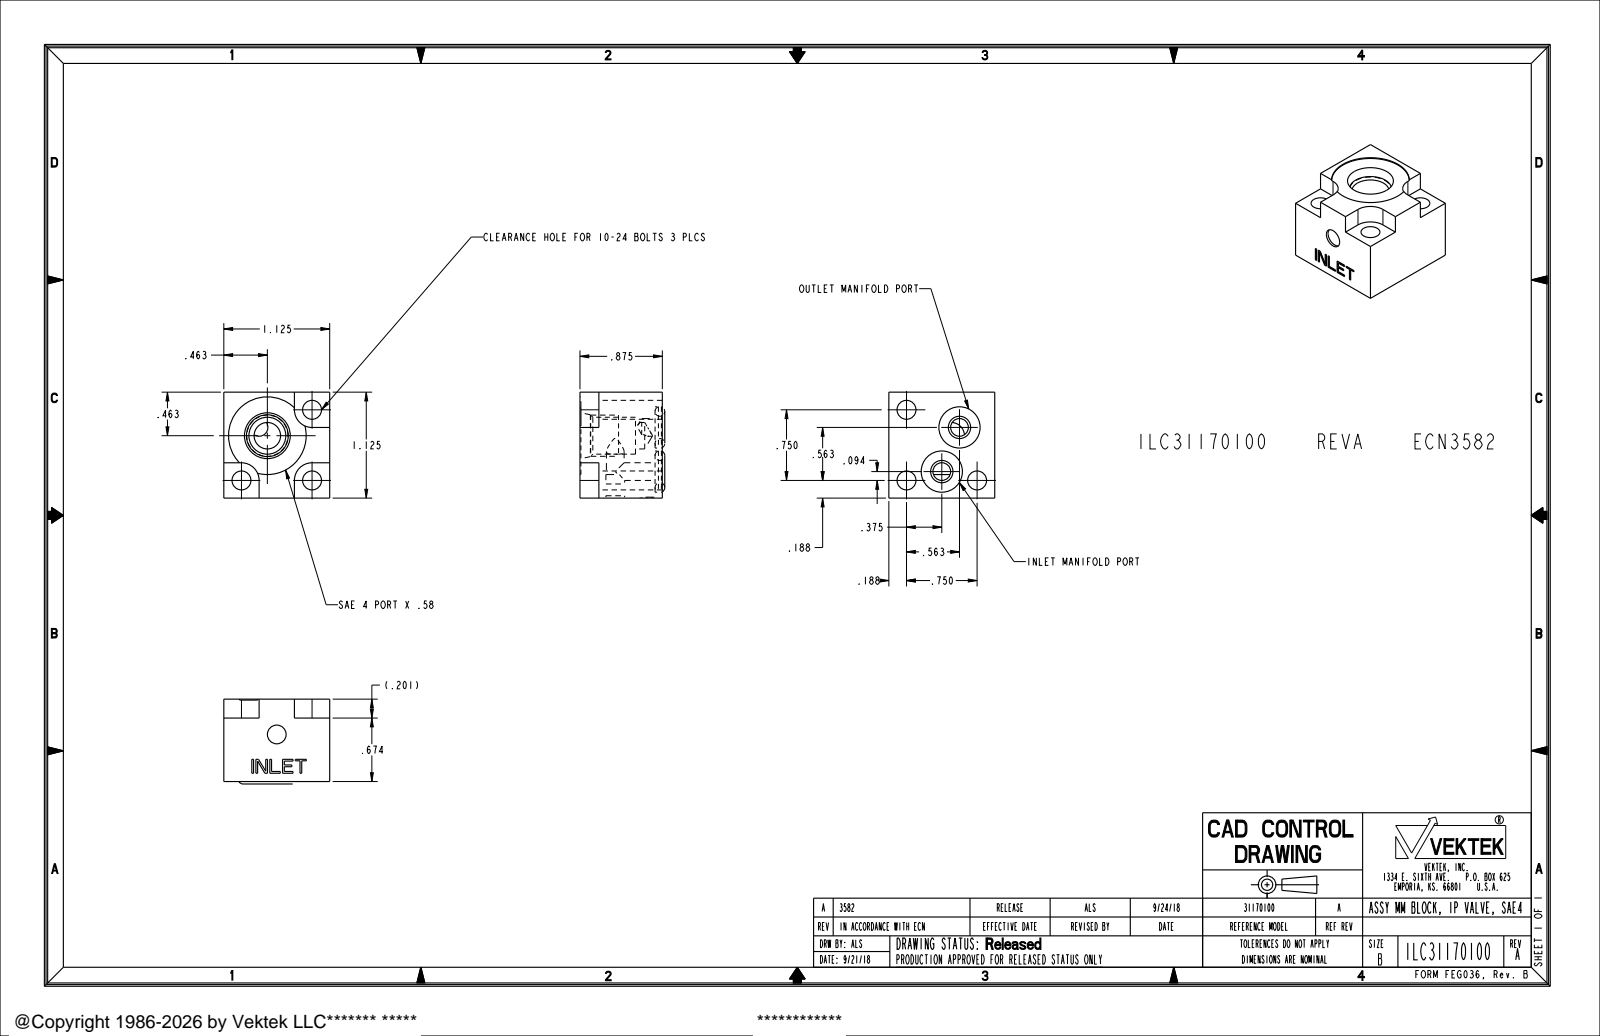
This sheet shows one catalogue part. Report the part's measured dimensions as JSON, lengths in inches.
{"part_name": "ILC31170100", "step_written_by": "PRO/ENGINEER BY PARAMETRIC TECHNOLOGY CORPORATION, 2013320 (AUTOMOTIVE_DESIGN)", "units": "inches", "bodies": {"solids": 1, "faces": 115, "planar": 69, "cylindrical": 35, "other": 11}, "overall_size": [1.125, 1.125, 0.901], "volume_in3": 0.845, "surface_area_in2": 9.914, "round_holes": [[0.188, 3], [0.201, 3], [0.438, 2], [0.199, 1], [0.281, 1], [0.392, 1], [0.825, 1]], "round_bosses_or_shafts": [[0.437, 1]], "partial_cylinders_radius": [[0.187, 3]], "face_to_face_distances": [1.125, 0.875, 0.865, 0.191, 0.674, 0.201, 0.077, 0.597, 0.788, 0.798], "hole_center_spacings": [0.386, 0.548, 0.593, 0.75, 0.125, 0.394, 0.506, 0.672]}
